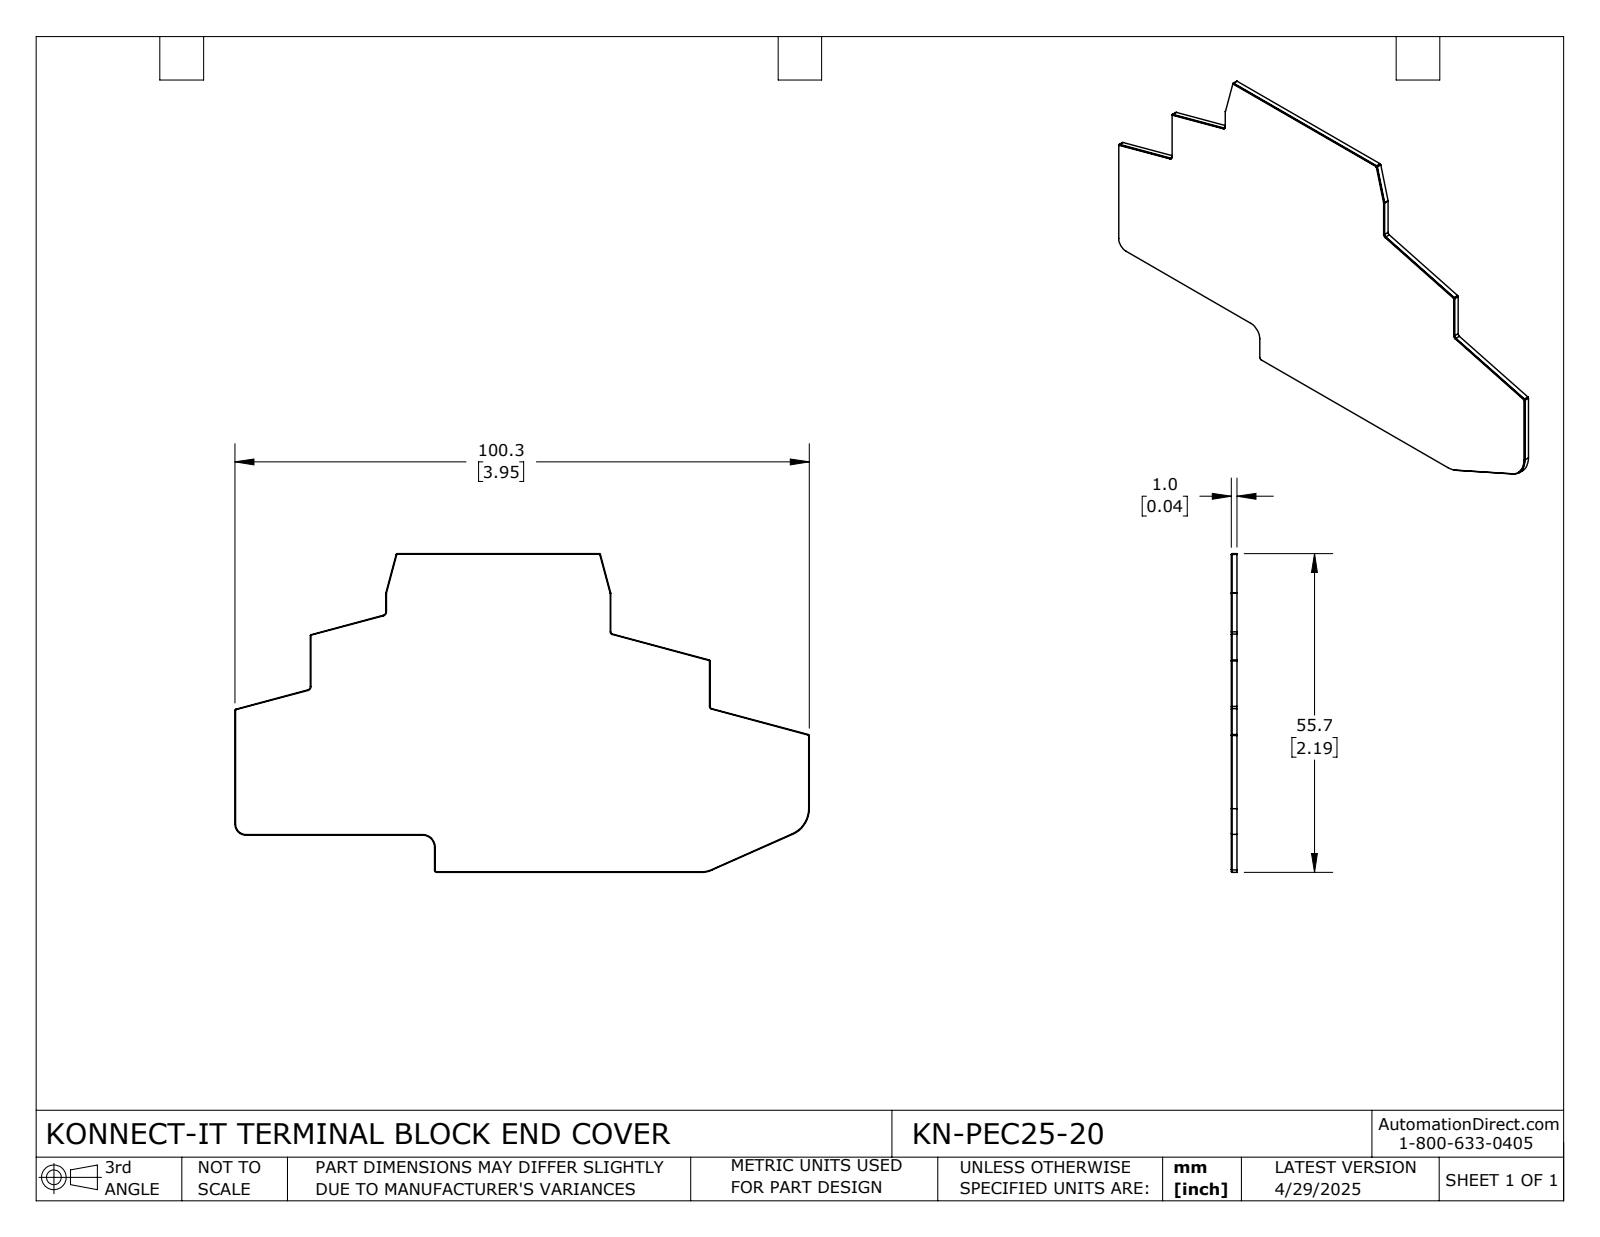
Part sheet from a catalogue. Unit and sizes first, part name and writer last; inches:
Units: inches
Overall size (bounding box): 3.948 × 2.191 × 0.039
Partial cylindrical surfaces — rounded edges, fillets, slot ends (radius × count): R0.004 ×8, R0.008 ×8, R0.016 ×3, R0.02 ×2, R0.024 ×2, R0.028 ×2, R0.189 ×2, R0.193 ×2
Main face-to-face distances: 0.039, 0.257, 2.191, 0.033, 1.935, 0.319, 0.361, 2.187, 3.948, 1.931
Volume: 0.243 in³ · Surface area: 12.78 in²
Bodies: 1 solid, 71 faces (37 planar, 34 cylindrical, 0 other)
Part name (STEP PRODUCT): KN-PEC25-20
STEP written by: SolidWorks 2024 (CONFIG_CONTROL_DESIGN)
